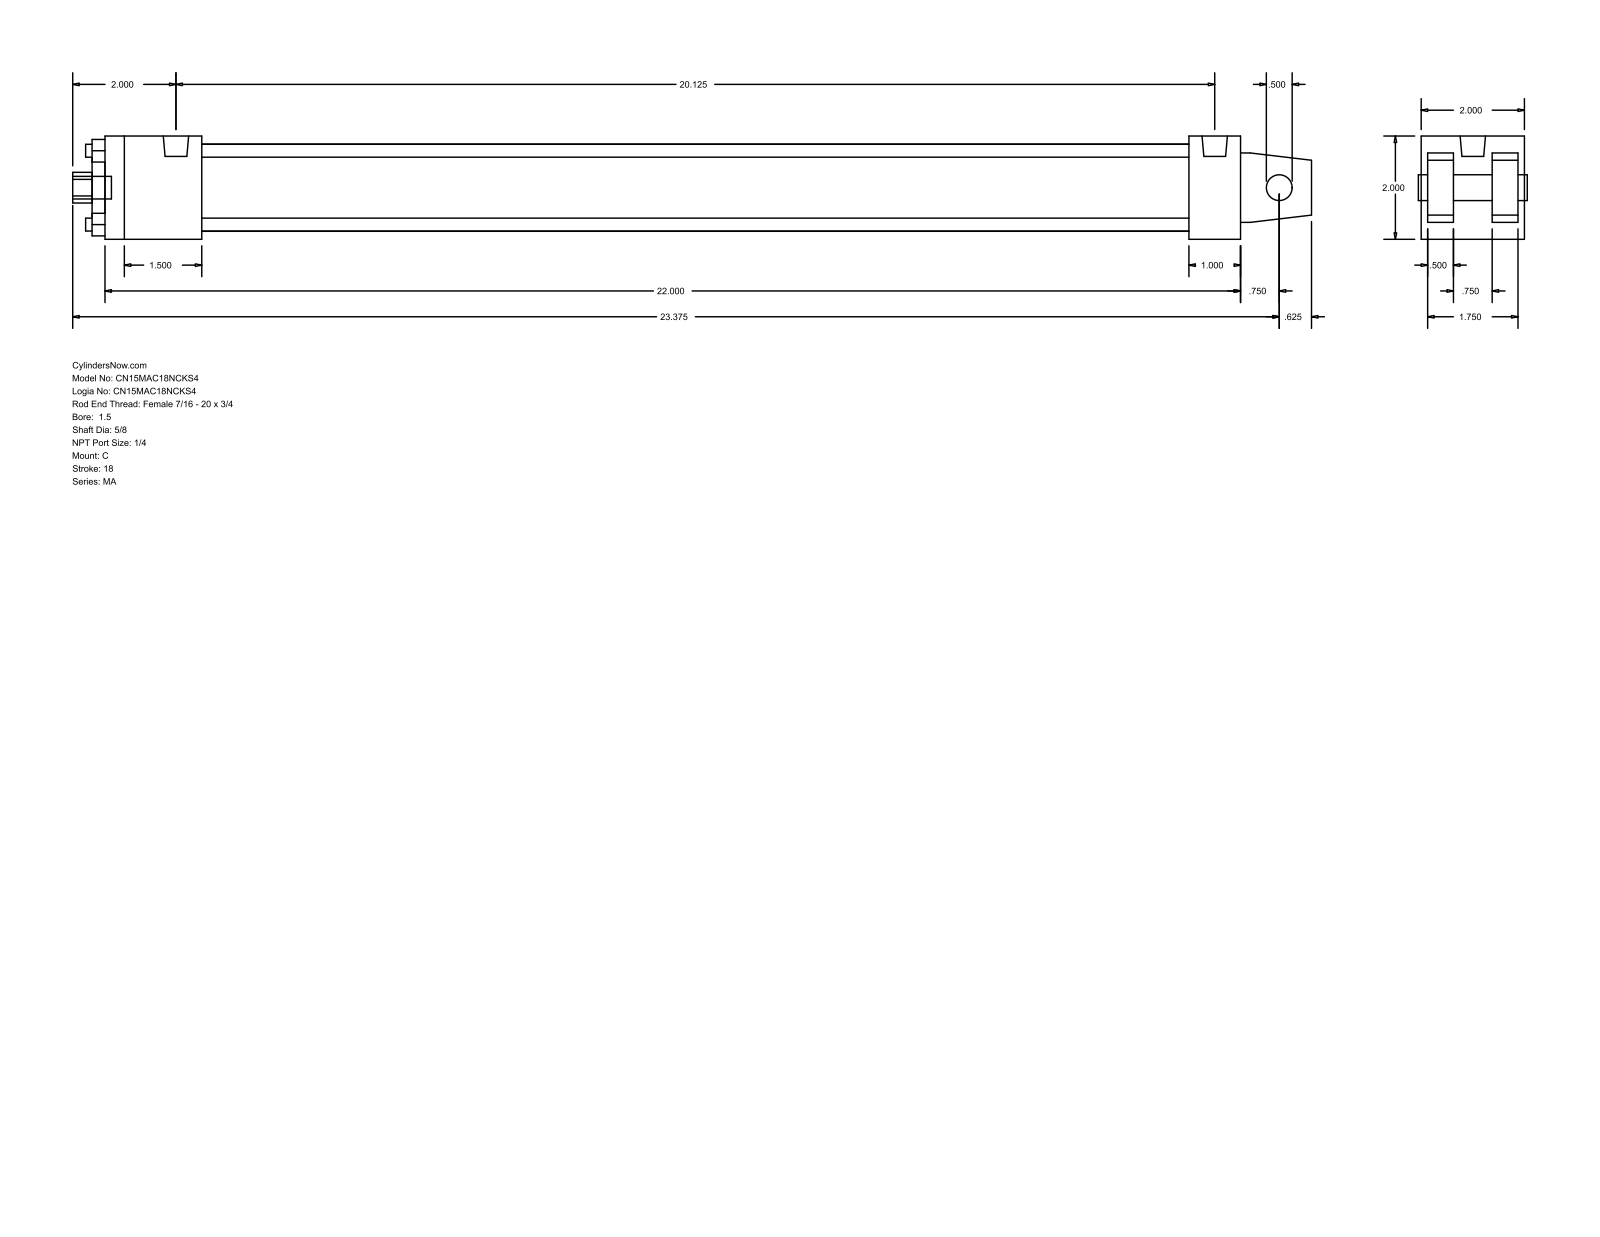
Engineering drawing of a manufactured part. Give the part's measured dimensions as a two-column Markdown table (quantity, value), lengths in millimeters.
| quantity | value |
| --- | --- |
| part name | MA_C__0150_0.625 |
| STEP written by | GSSL Pune (CONFIG_CONTROL_DESIGN) |
| units | millimeters |
| bodies | 0 solids, 103 faces (76 planar, 27 cylindrical, 0 other) |
| overall size | 609.6 × 50.8 × 50.8 |
| round holes (diameter × count) | 6.35 × 4, 12.7 × 1, 15.88 × 1, 28.57 × 1, 42.93 × 1 |
| round bosses / shafts (diameter × count) | 7.94 × 4, 12.49 × 2, 11.11 × 1 |
| partial cylindrical surfaces (radius × count) | 7.54 × 1 |
| main face-to-face distances | 50.8, 34.93, 12.7, 3.17, 15.87, 47.63, 31.76, 558.79, 533.39, 25.4 |
| hole center spacings | 25.68, 36.32, 51.36 |
